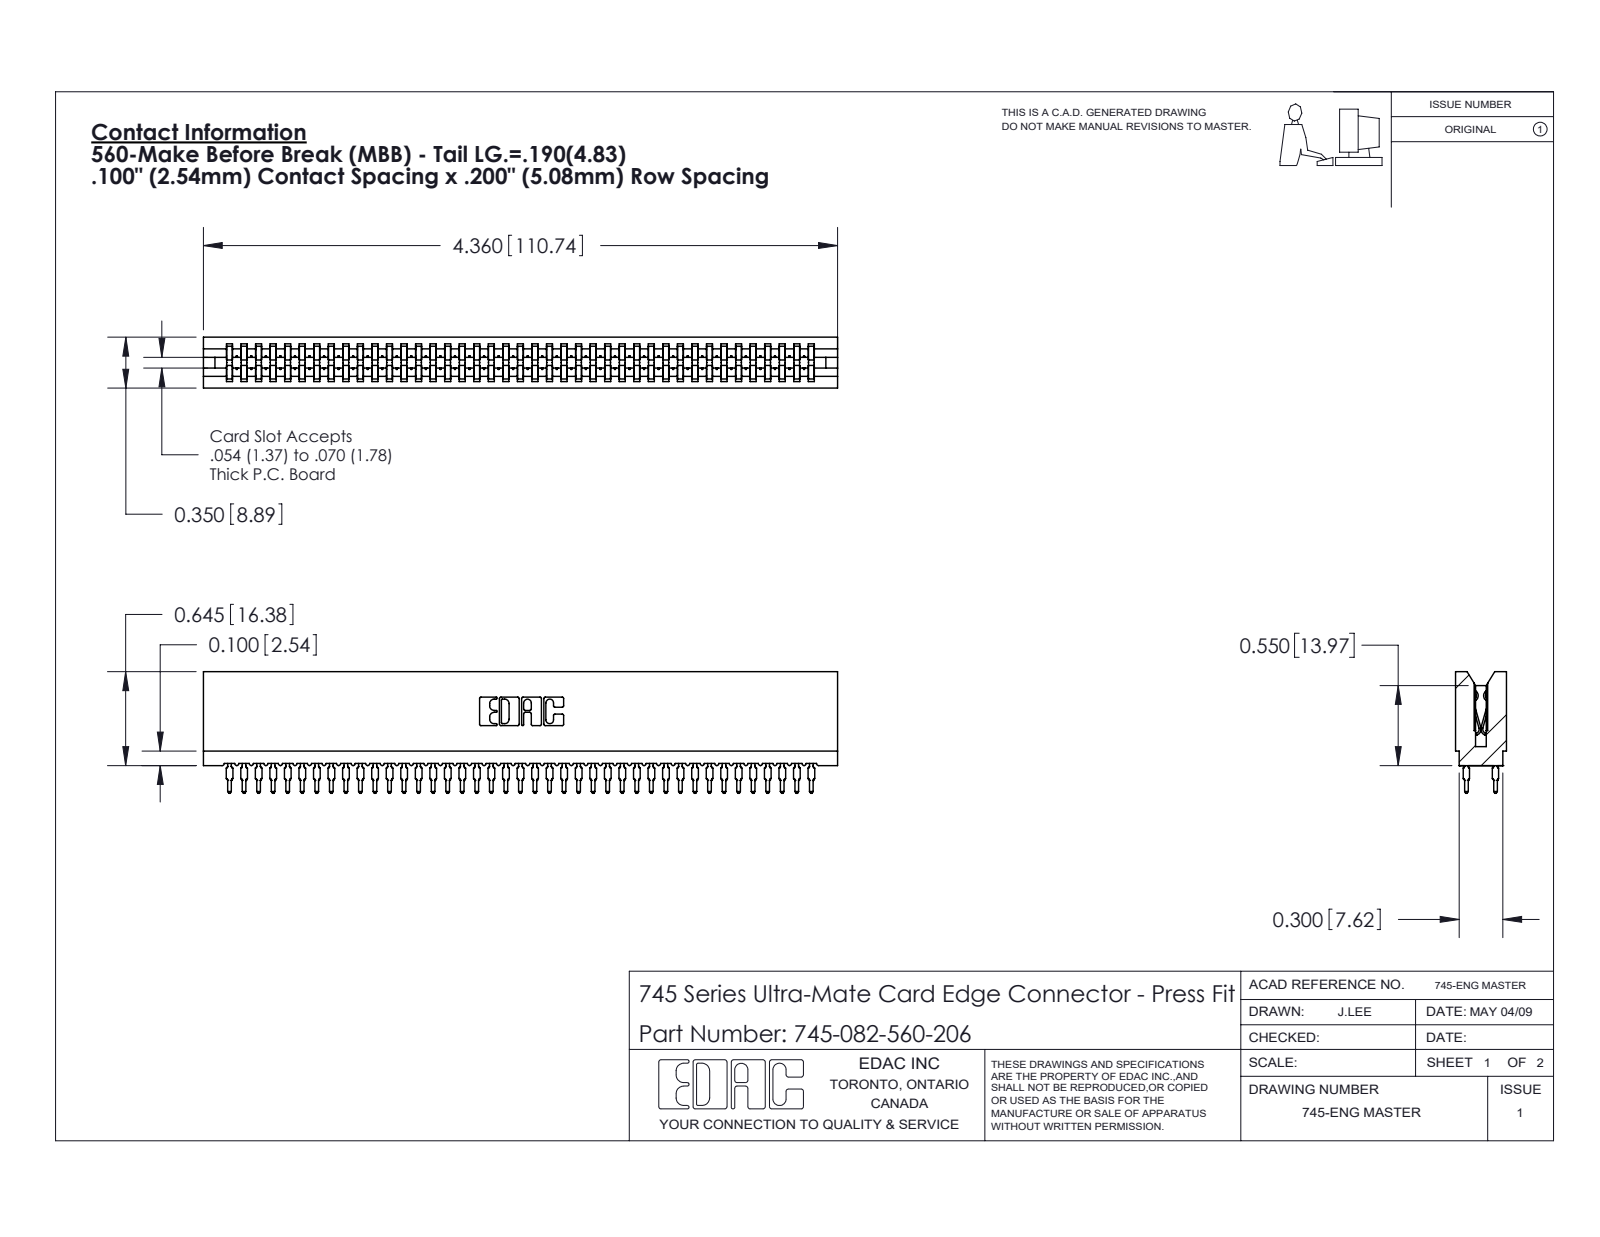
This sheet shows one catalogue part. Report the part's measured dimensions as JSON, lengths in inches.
{"part_name": "745-292-001_560; 745 Part_Insulator Option - 06; 745-082-560-206", "step_written_by": "SolidWorks 2020 (CONFIG_CONTROL_DESIGN)", "units": "inches", "bodies": {"solids": 83, "faces": 8173, "planar": 4238, "cylindrical": 1803, "other": 2132}, "overall_size": [4.36, 0.836, 0.35], "volume_in3": 0.626, "surface_area_in2": 34.34, "partial_cylinders_radius": [[0.021, 164], [0.015, 82], [0.01, 22], [0.005, 8], [0.011, 8], [0.007, 6], [0.031, 6], [0.026, 3]], "face_to_face_distances": [0.35, 0.063, 0.287, 0.2, 0.138, 0.212, 0.076, 0.149, 0.045, 0.305]}
